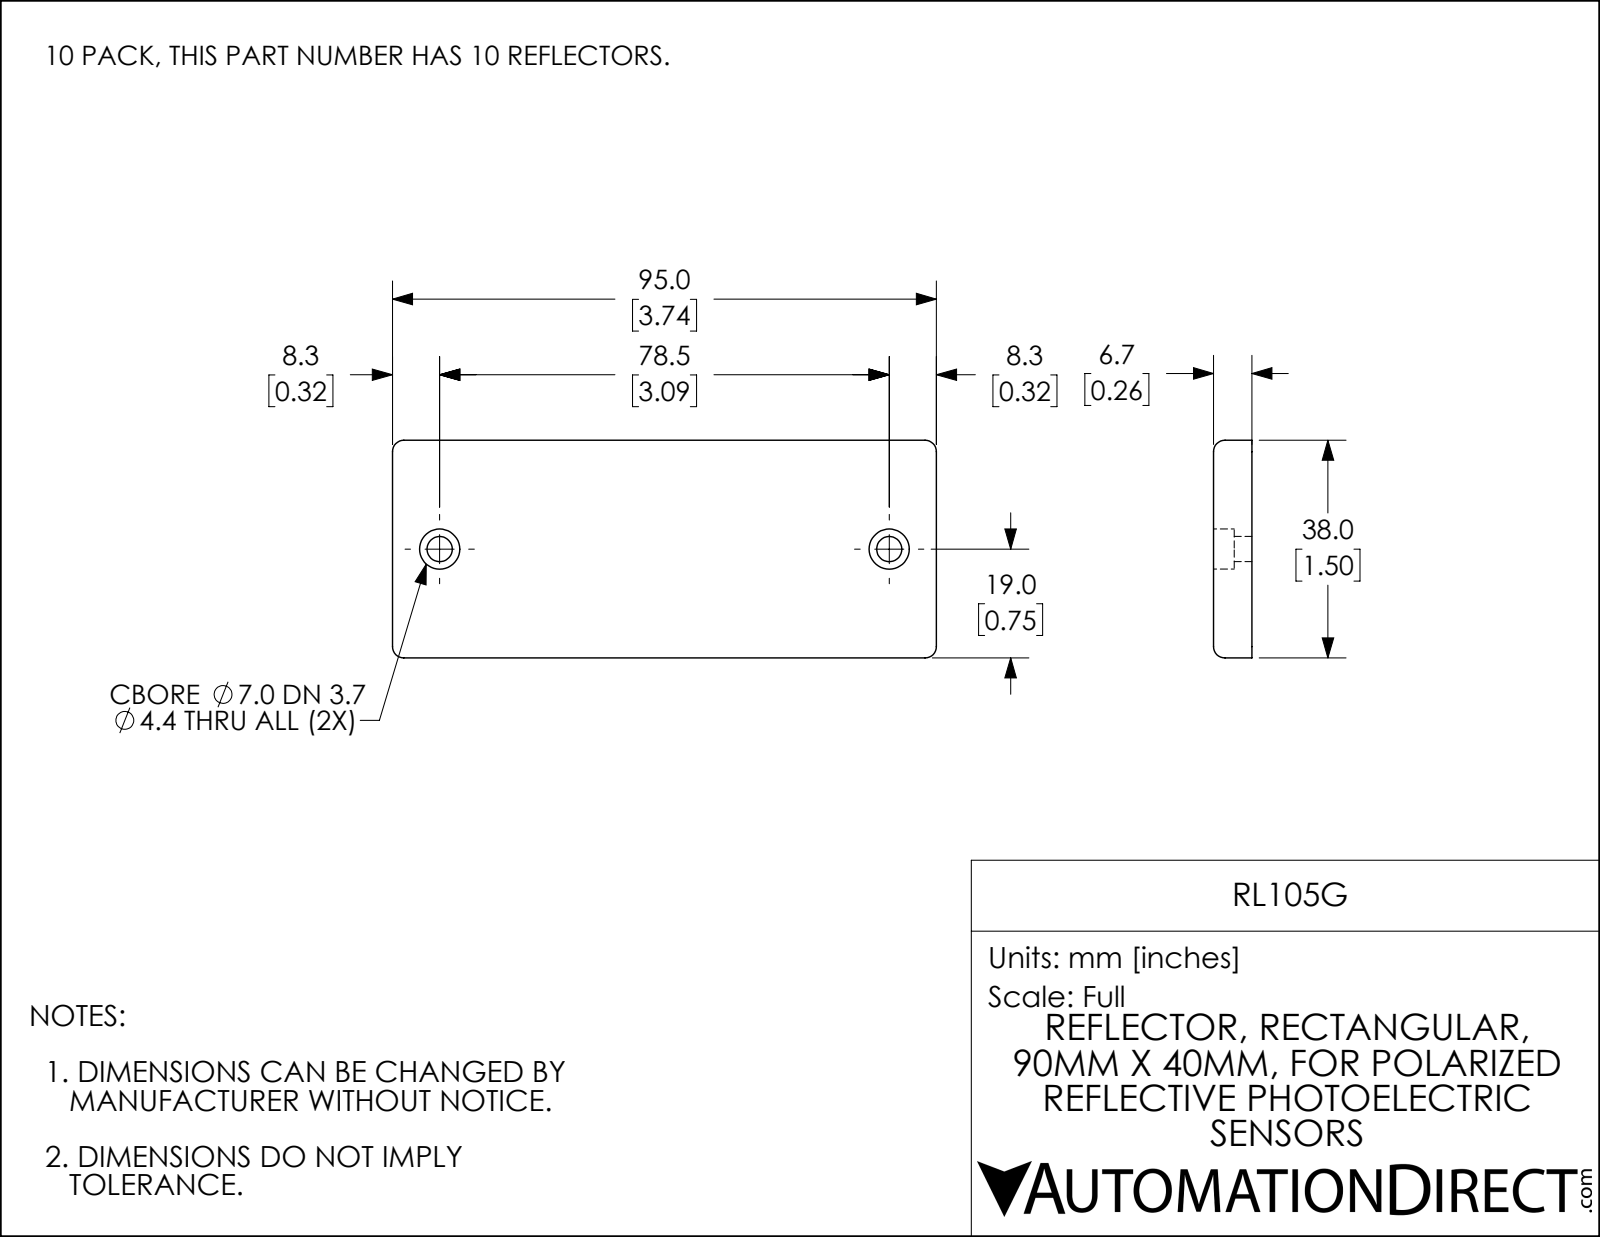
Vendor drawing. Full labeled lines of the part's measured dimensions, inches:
Part name (STEP PRODUCT): RL105G
STEP written by: SolidWorks 2017 (AUTOMOTIVE_DESIGN)
Units: inches
Bodies: 1 solid, 24 faces (8 planar, 12 cylindrical, 4 other)
Overall size (bounding box): 3.74 × 1.496 × 0.264
Volume: 1.438 in³ · Surface area: 13.84 in²
Round holes (diameter × count): ⌀0.173 ×2, ⌀0.276 ×2
Partial cylindrical surfaces — rounded edges, fillets, slot ends (radius × count): R0.079 ×8
Main face-to-face distances: 0.264, 1.496, 3.74, 0.122, 0.142
Hole centre spacings: 3.091
